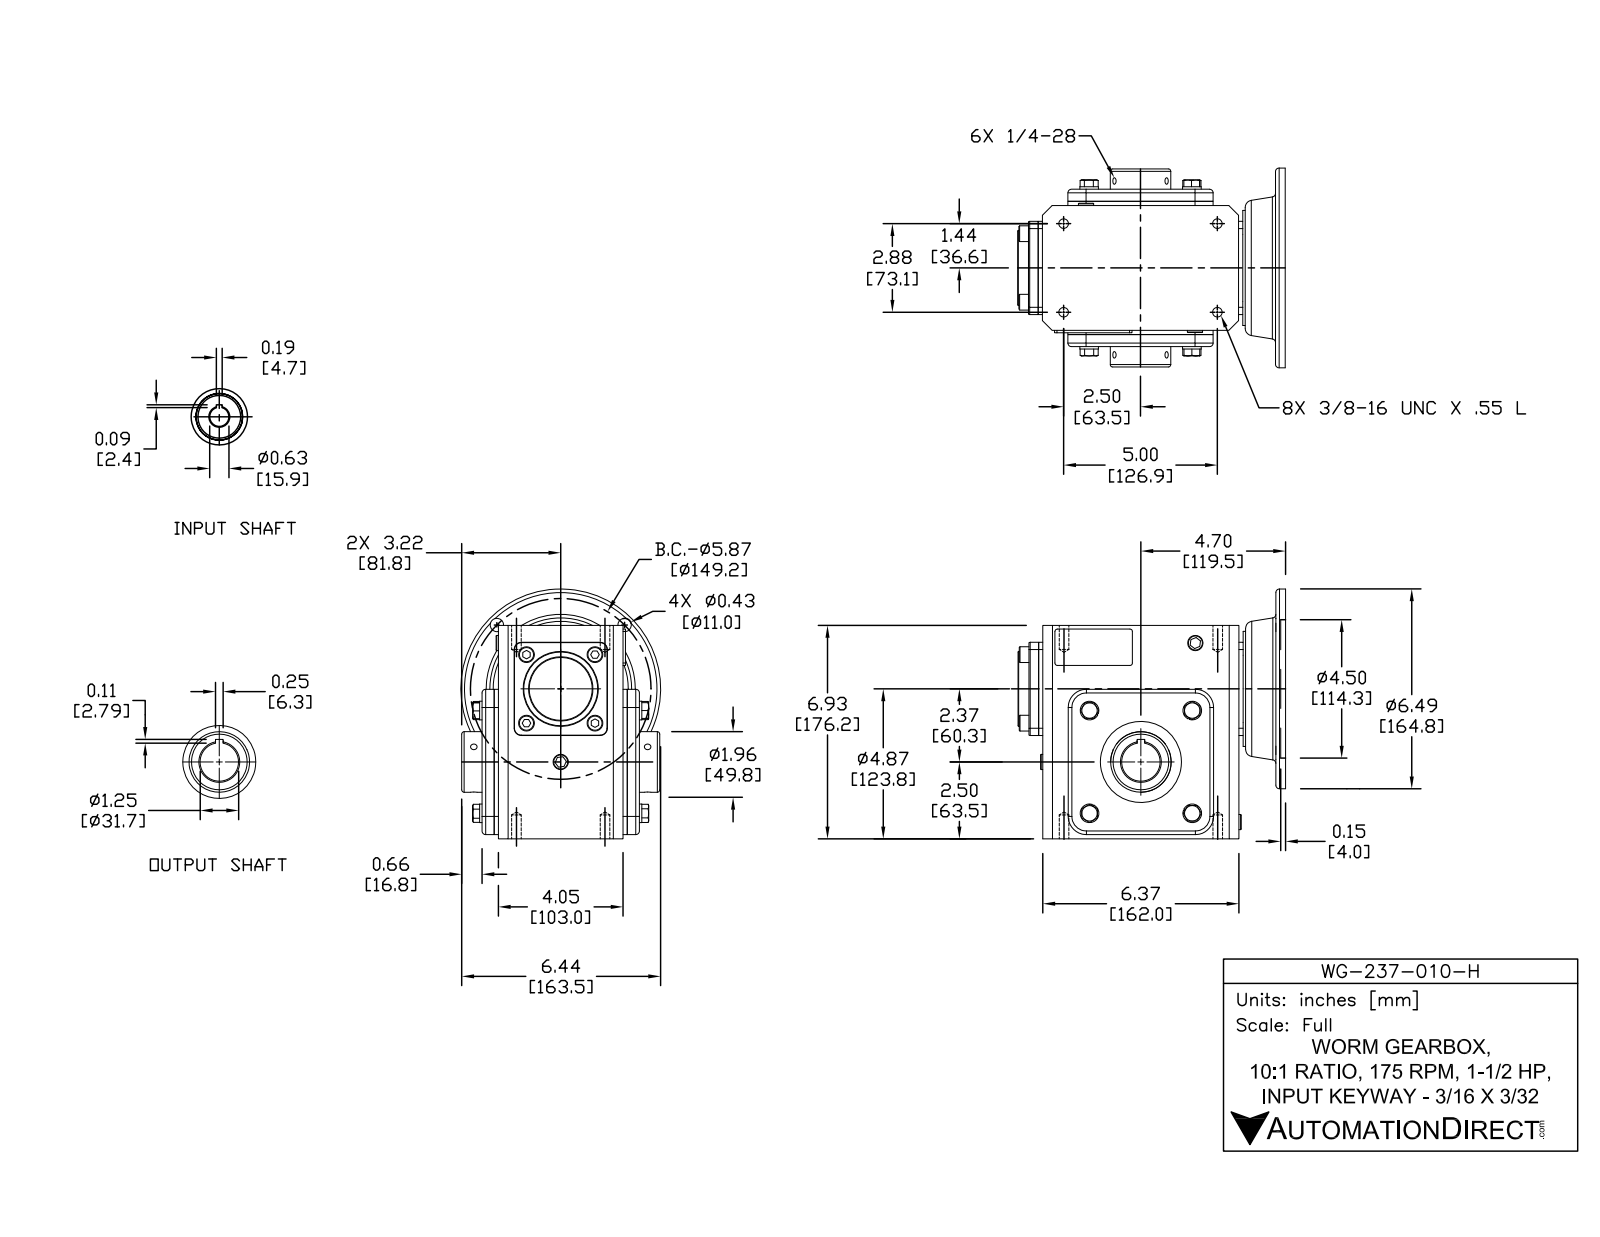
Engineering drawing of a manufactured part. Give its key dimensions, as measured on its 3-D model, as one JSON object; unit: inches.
{"part_name": "WG-237-010-H", "step_written_by": "SolidWorks 2015 (CONFIG_CONTROL_DESIGN)", "units": "inches", "bodies": {"solids": 37, "faces": 609, "planar": 348, "cylindrical": 172, "other": 89}, "overall_size": [8.701, 8.123, 6.496], "volume_in3": 217.1, "surface_area_in2": 540.6, "round_holes": [[0.213, 6], [0.313, 4], [0.406, 4], [0.591, 1], [0.625, 1], [1.181, 1], [1.25, 1], [1.457, 1], [1.969, 1], [2.638, 1], [3.819, 1], [4.5, 1]], "round_bosses_or_shafts": [[0.606, 4], [0.512, 4], [6.496, 1], [3.74, 1], [2.441, 1], [2.047, 1], [1.142, 1]], "partial_cylinders_radius": [[0.079, 8], [0.118, 8], [0.236, 6], [0.591, 4], [0.02, 2], [0.039, 2]], "face_to_face_distances": [0.138, 4.331, 4.724, 0.531, 0.394, 4.193, 4.587, 6.516, 0.315, 6.937], "hole_center_spacings": [2.859, 2.937, 4.945, 5.653, 2.098, 2.88, 4.154, 4.154]}
